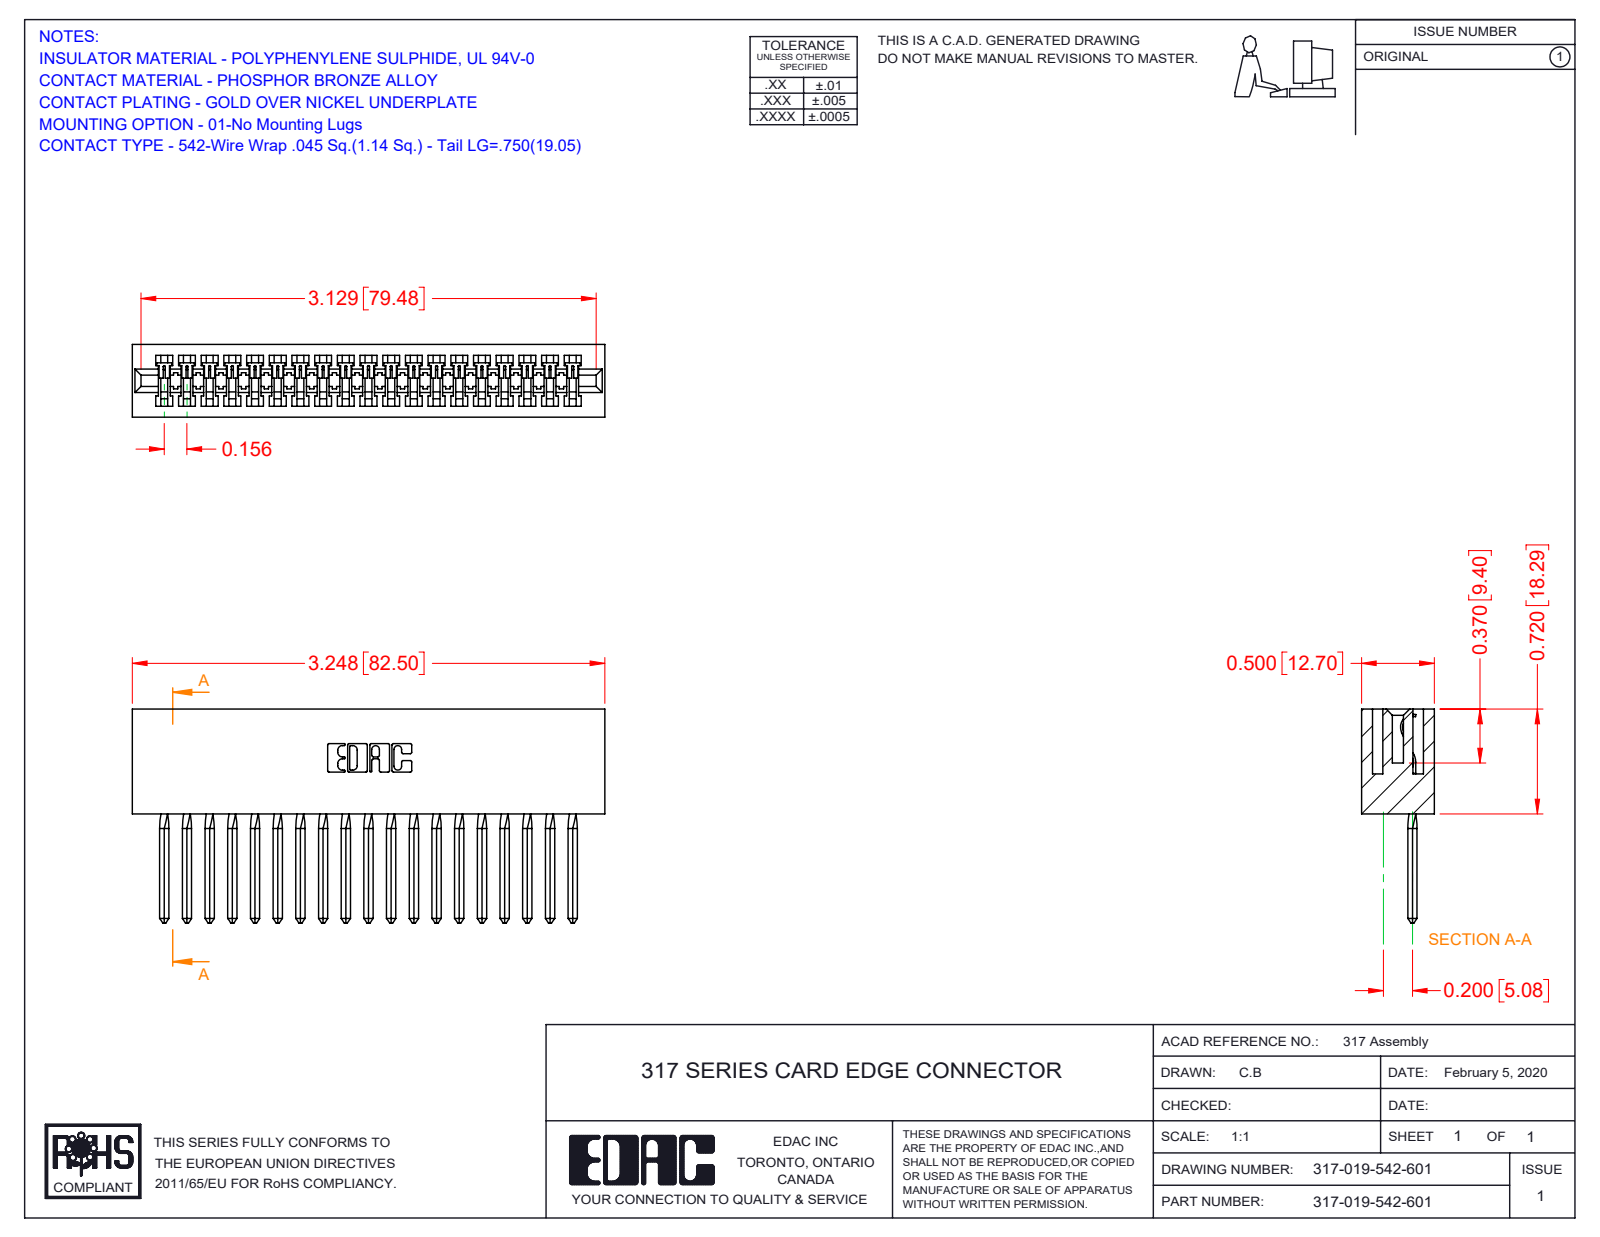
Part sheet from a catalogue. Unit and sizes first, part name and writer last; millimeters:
Units: millimetres
Overall size (bounding box): 82.5 × 37.3 × 12.7
Partial cylindrical surfaces — rounded edges, fillets, slot ends (radius × count): R0.2 ×38, R0.3 ×22, R0.2 ×6, R0.8 ×6, R0.7 ×3, R1.9 ×1, R2.3 ×1, R2.5 ×1
Main face-to-face distances: 12.7, 1.9, 10.8, 8.9, 2.8, 3.5, 18.3, 7.1, 4, 5.4
Volume: 13 700 mm³ · Surface area: 16 260 mm²
Bodies: 20 solids, 1515 faces (1266 planar, 173 cylindrical, 76 other)
Part name (STEP PRODUCT): 317-290-003_542; 317 Part_Lugless; 317-019-542-601
STEP written by: SolidWorks 2016 (CONFIG_CONTROL_DESIGN)
